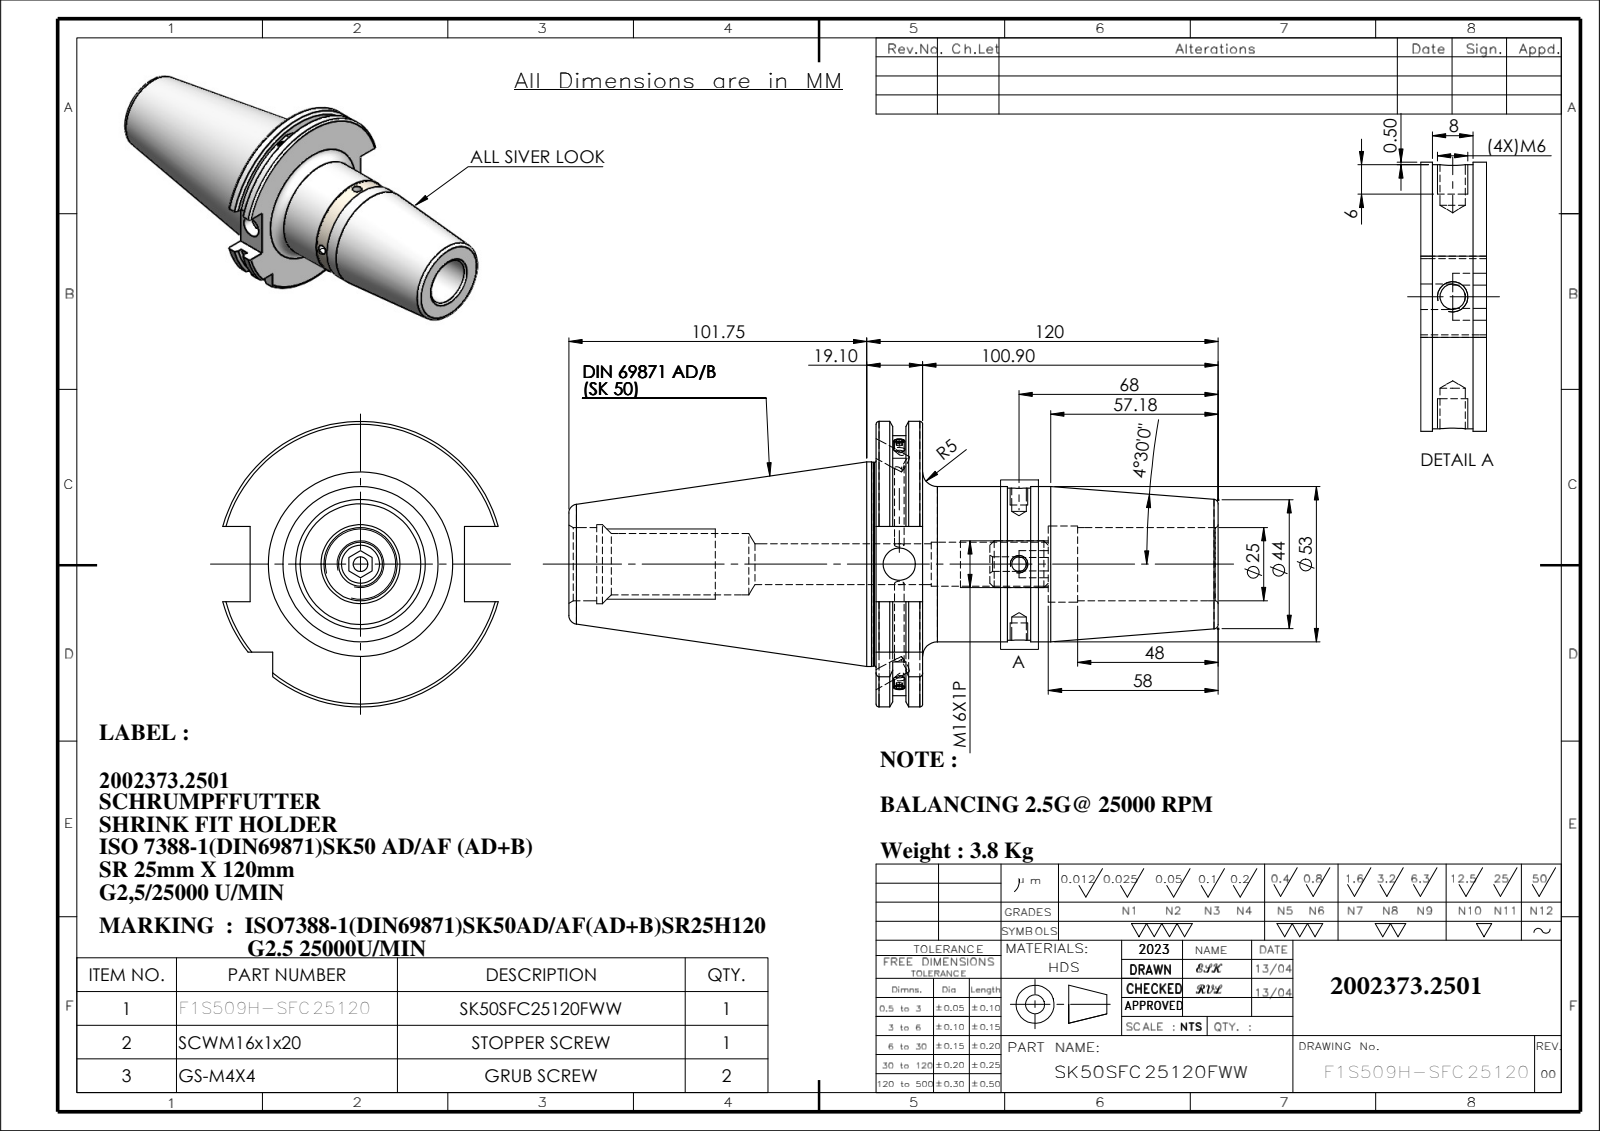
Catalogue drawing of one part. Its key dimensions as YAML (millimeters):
part_name: "91506-SR225120; SK50SFC25120FWW; Copy of M4X4_DIN 913 - M4 x 4-N; SCWM16X1P"
step_written_by: "SolidWorks 2018 (CONFIG_CONTROL_DESIGN)"
units: millimeters
bodies: {solids: 4, faces: 184, planar: 55, cylindrical: 67, other: 62}
overall_size: [221.75, 97.5, 94.05]
volume: 497595
surface_area: 68020
round_holes:
  - {diameter: 5, count: 3}
  - {diameter: 6, count: 2}
  - {diameter: 3.3, count: 1}
  - {diameter: 11, count: 1}
  - {diameter: 14, count: 1}
  - {diameter: 15, count: 1}
  - {diameter: 21, count: 1}
  - {diameter: 25, count: 1}
  - {diameter: 26, count: 1}
  - {diameter: 27, count: 1}
round_bosses_or_shafts:
  - {diameter: 4, count: 2}
  - {diameter: 69.85, count: 1}
  - {diameter: 69.45, count: 1}
  - {diameter: 53, count: 1}
  - {diameter: 52, count: 1}
  - {diameter: 16, count: 1}
partial_cylinders:
  - {radius: 44.9, count: 1}
  - {radius: 48.75, count: 1}
face_to_face_distances: [15.9, 116.8, 100.9, 5.66, 10.24, 111.14, 10.15, 4.49, 5.75, 106.65]
hole_center_spacings: [40.9]
